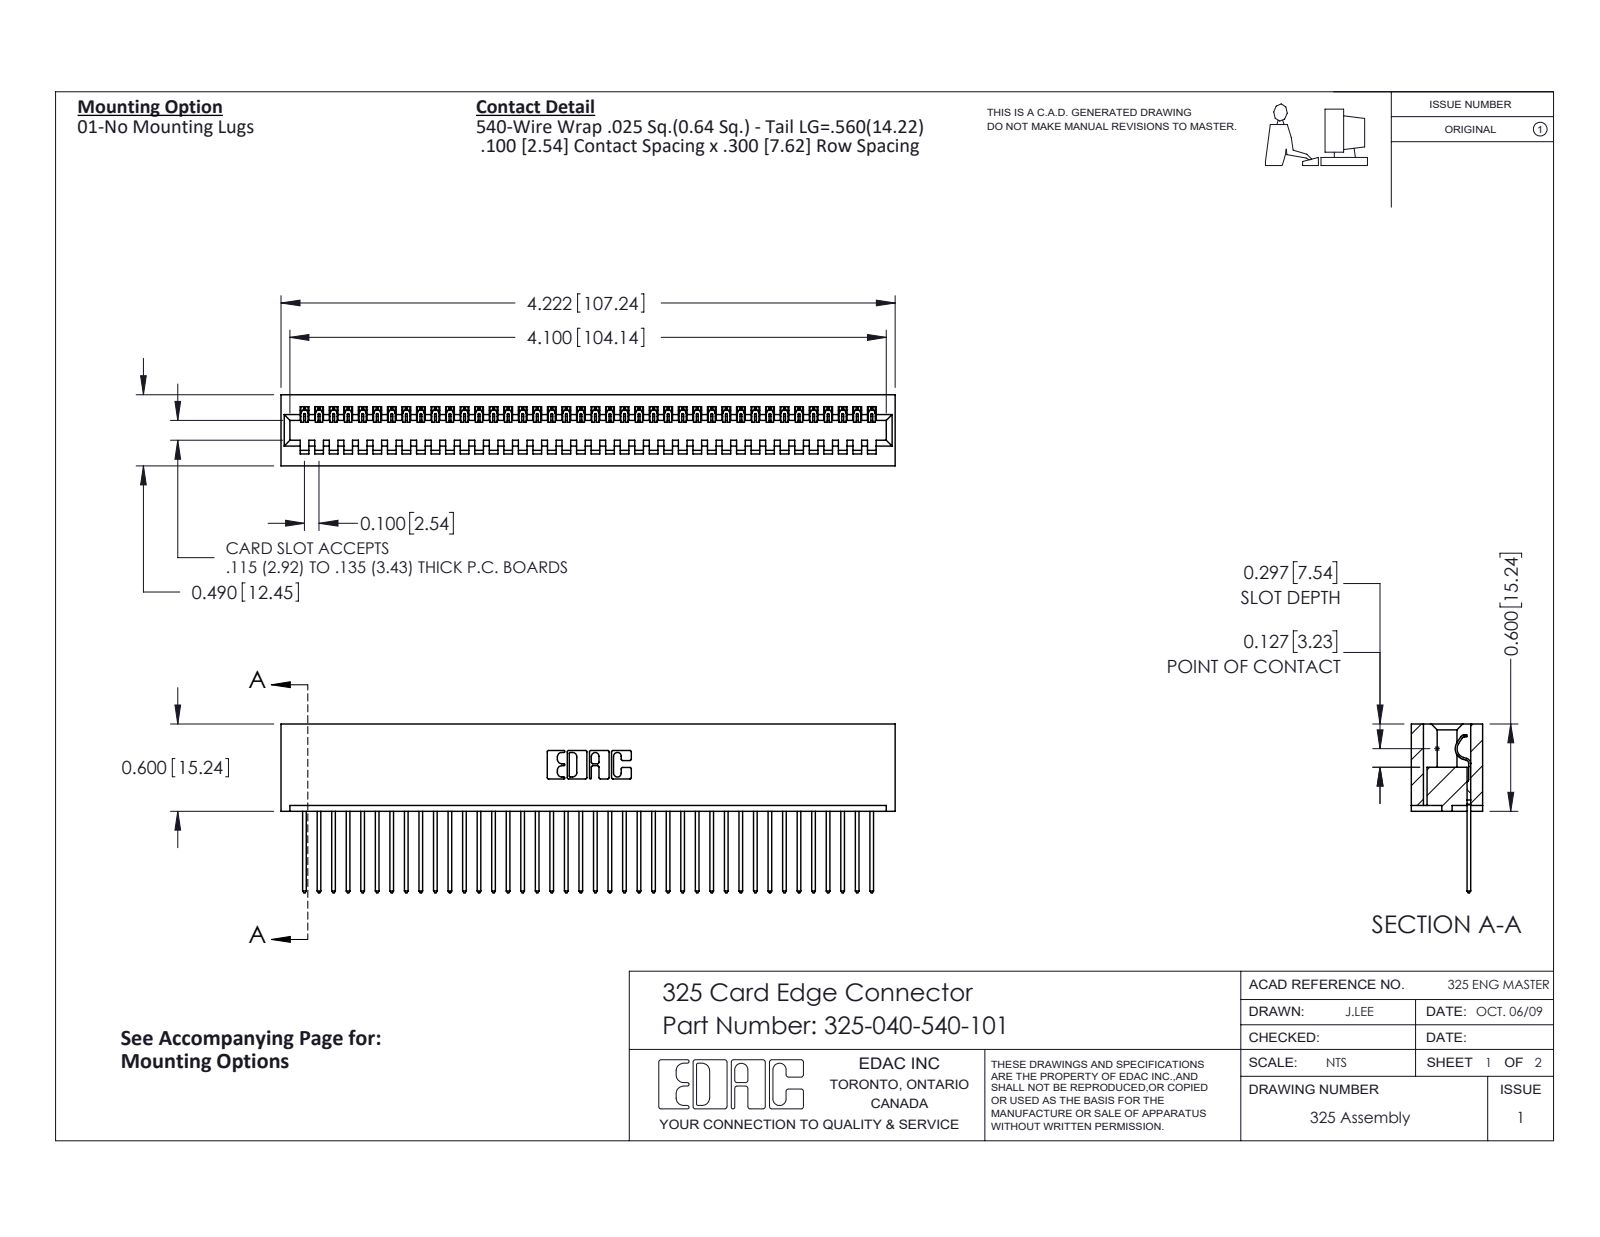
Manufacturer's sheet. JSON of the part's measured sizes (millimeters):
{"part_name": "325 Part_Lugless; 325-040-540-101; 325-292-001_325-293-140", "step_written_by": "SolidWorks 2016 (CONFIG_CONTROL_DESIGN)", "units": "millimeters", "bodies": {"solids": 41, "faces": 2426, "planar": 1746, "cylindrical": 680, "other": 0}, "overall_size": [107.2, 29.5, 12.4], "volume_mm3": 14200, "surface_area_mm2": 16400, "partial_cylinders_radius": [[0.2, 80], [0.3, 80], [0.3, 22], [0.2, 6], [0.8, 6], [0.7, 3], [0.4, 1], [0.6, 1]], "face_to_face_distances": [2.1, 10.3, 7.6, 12.4, 2.7, 9.7, 0.6, 8.3, 14.2, 6.7]}
